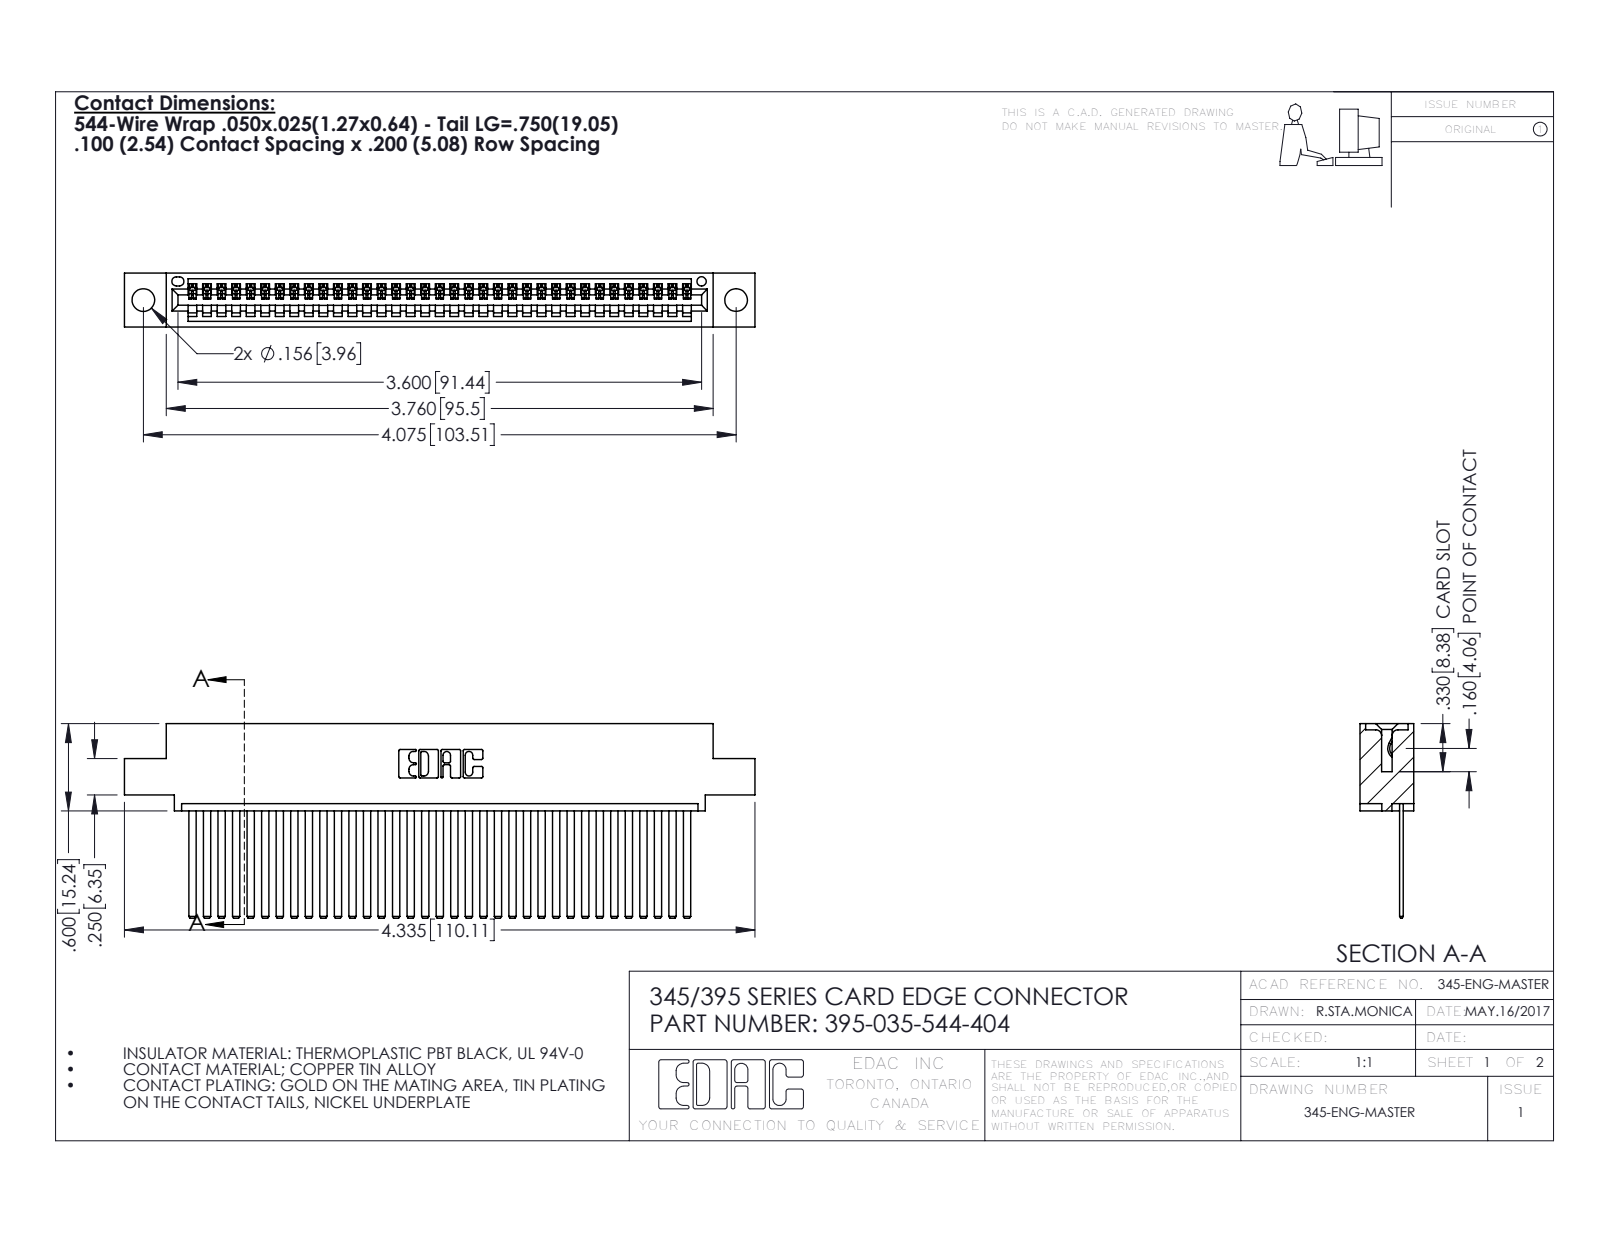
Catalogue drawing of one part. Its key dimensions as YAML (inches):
part_name: "345-292-001_345-293-144; 395-035-544-404; 345 Part_0.110 Offset - 0.156 Dia-TH"
step_written_by: "SolidWorks 2016 (CONFIG_CONTROL_DESIGN)"
units: inches
bodies: {solids: 36, faces: 1950, planar: 1344, cylindrical: 606, other: 0}
overall_size: [4.335, 1.337, 0.37]
volume: 0.65
surface_area: 23.5
round_holes:
  - {diameter: 0.156, count: 2}
  - {diameter: 0.064, count: 1}
partial_cylinders:
  - {radius: 0.006, count: 70}
  - {radius: 0.01, count: 22}
  - {radius: 0.007, count: 6}
  - {radius: 0.031, count: 6}
  - {radius: 0.026, count: 3}
  - {radius: 0.031, count: 2}
  - {radius: 0.04, count: 2}
  - {radius: 0.014, count: 1}
face_to_face_distances: [0.072, 0.298, 0.025, 0.098, 0.272, 0.37, 0.2, 0.225, 0.149, 0.072]
hole_center_spacings: [0.27, 3.839, 4.075]
